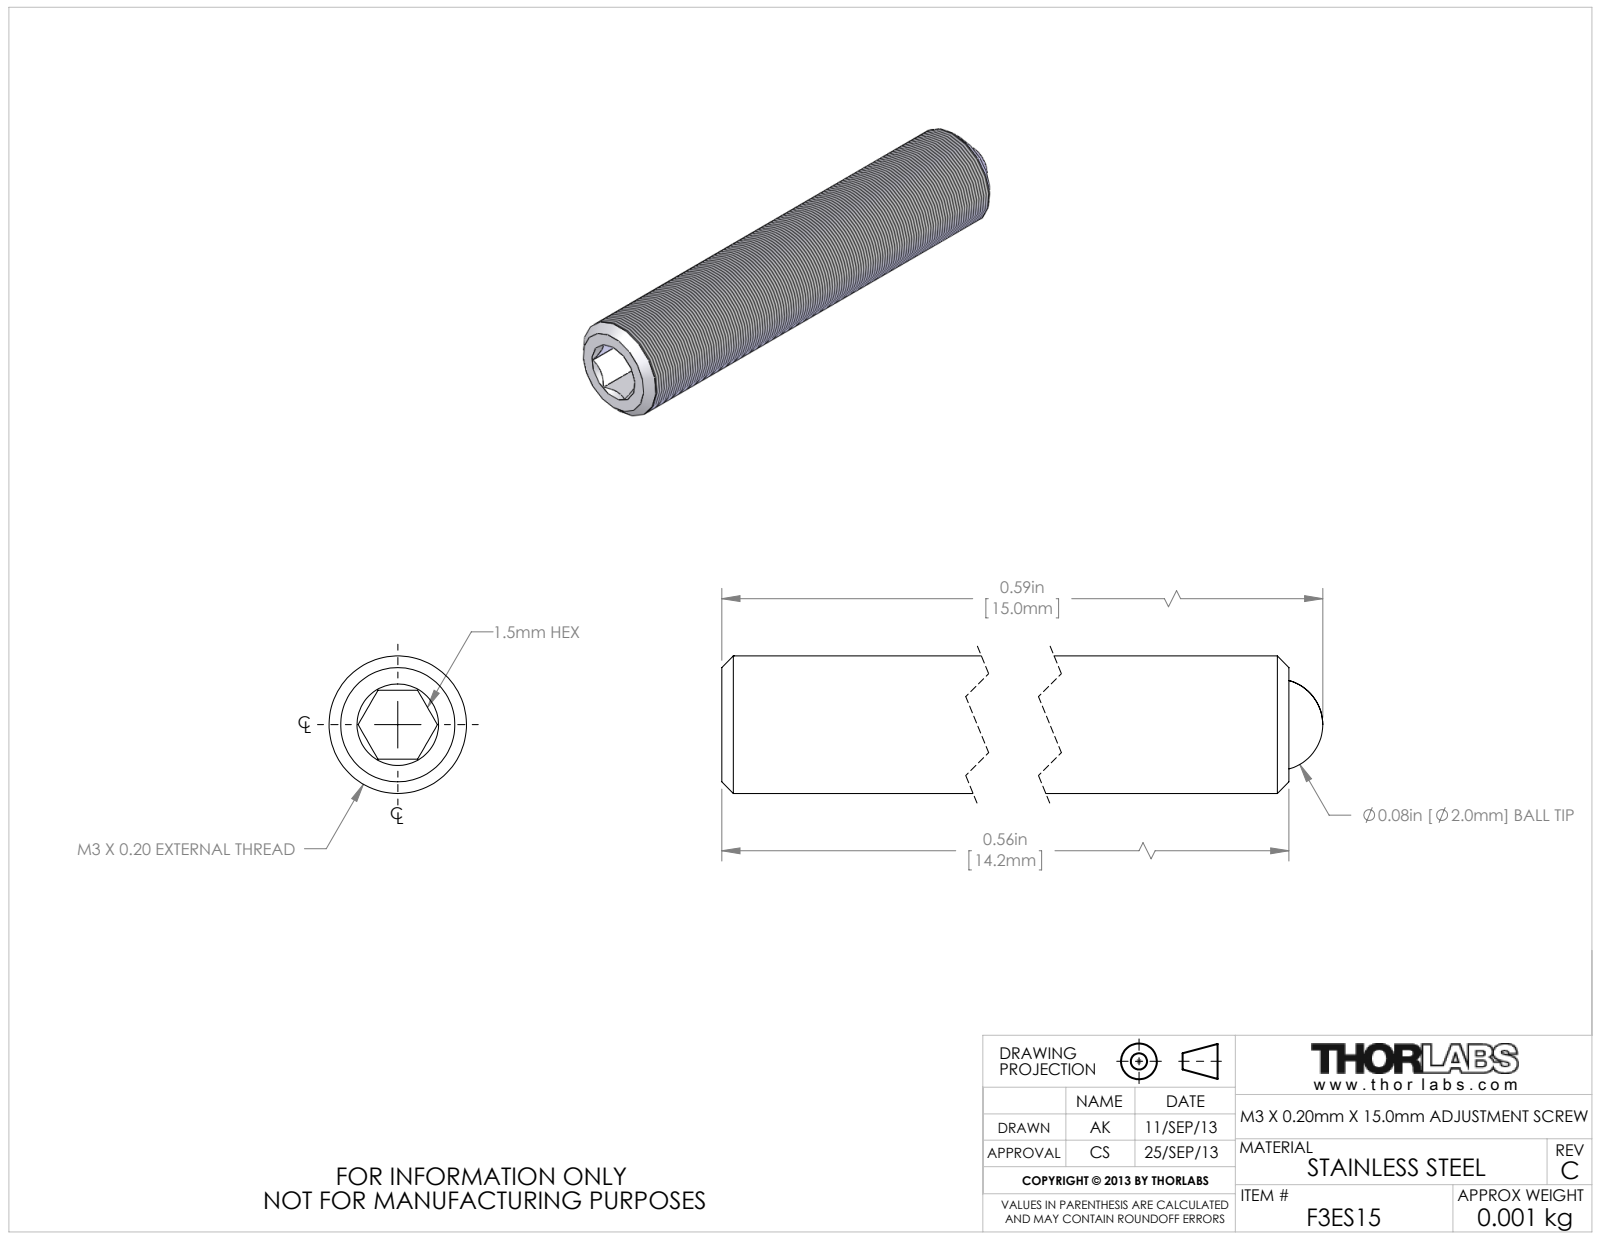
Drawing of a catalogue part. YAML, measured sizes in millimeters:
part_name: "8566-E0W"
step_written_by: "SolidWorks 2012 (AUTOMOTIVE_DESIGN)"
units: millimeters
bodies: {solids: 2, faces: 25, planar: 9, cylindrical: 4, other: 12}
overall_size: [15, 3, 3]
volume: 100
surface_area: 179
round_holes:
  - {diameter: 2, count: 1}
round_bosses_or_shafts:
  - {diameter: 3, count: 1}
face_to_face_distances: [1.5, 3, 11.2, 14.2]
